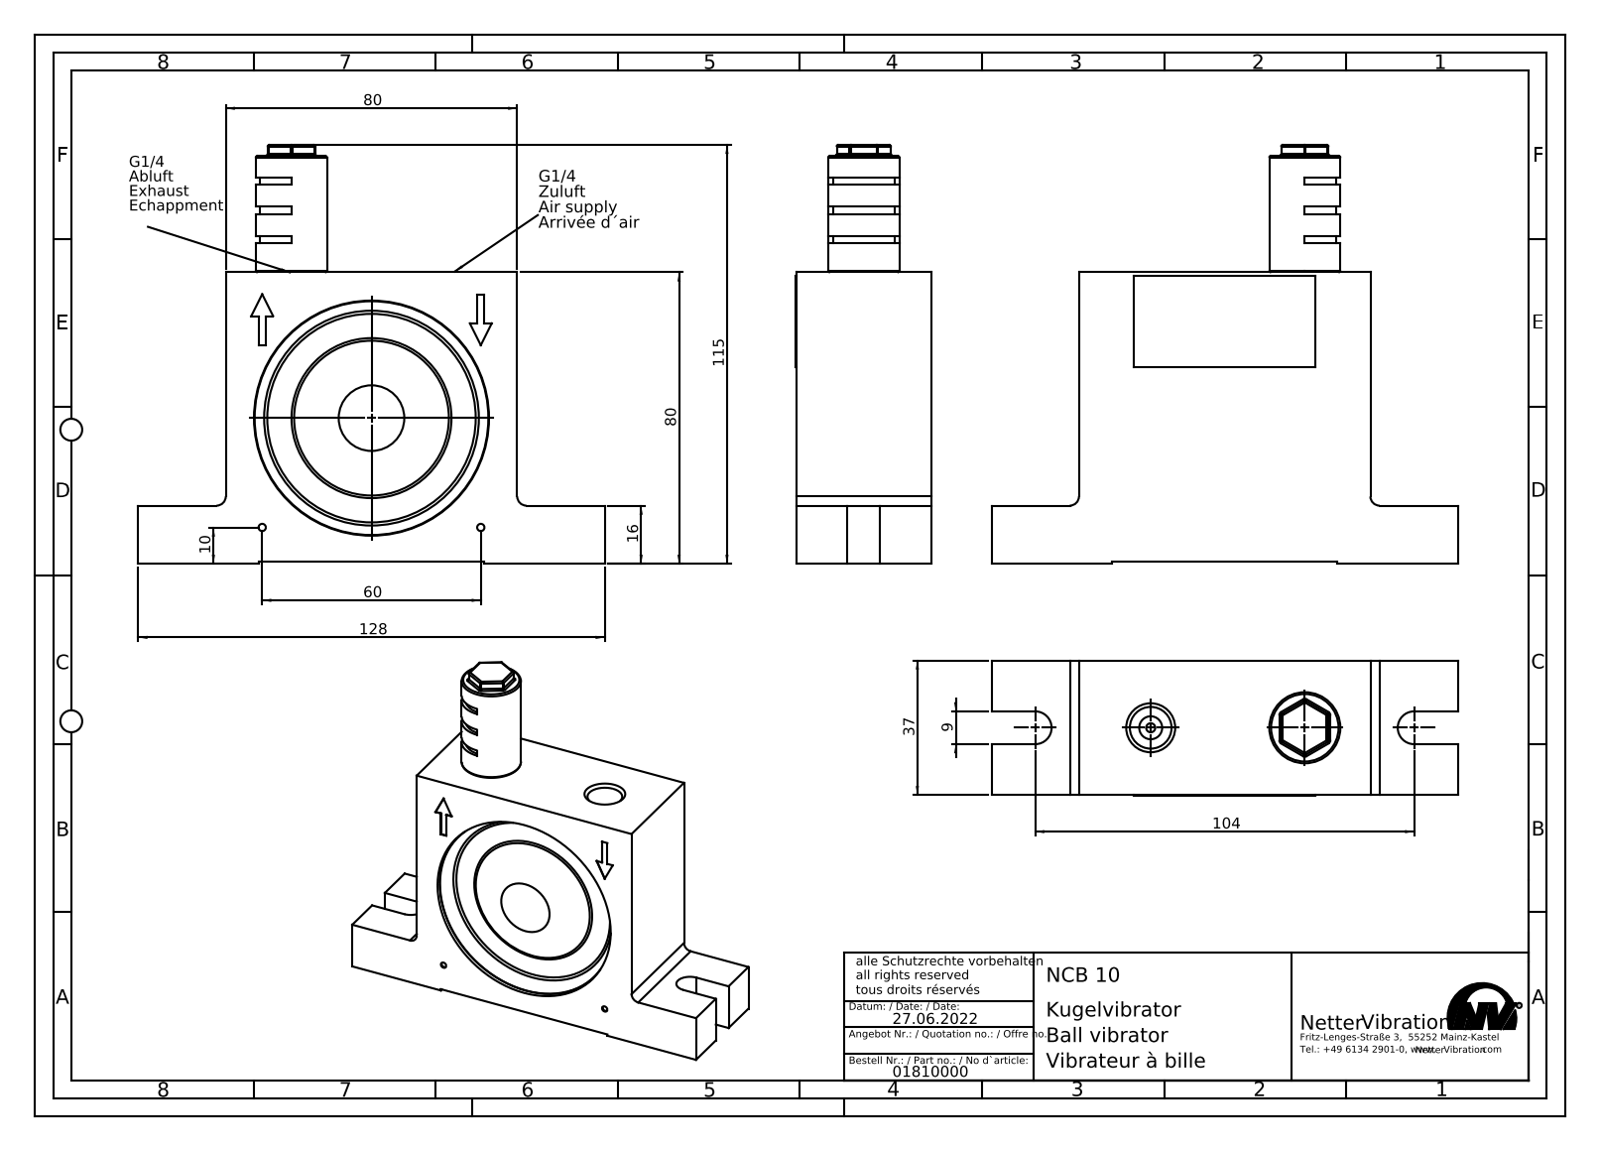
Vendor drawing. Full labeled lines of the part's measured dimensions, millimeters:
Part name (STEP PRODUCT): NCB 10 Kugelvibrator # 01810000
STEP written by: SolidWorks 2015 (AUTOMOTIVE_DESIGN)
Units: millimetres
Bodies: 3 solids, 232 faces (104 planar, 54 cylindrical, 74 other)
Overall size (bounding box): 128 × 115 × 37
Volume: 186 852 mm³ · Surface area: 47 803 mm²
Round holes (diameter × count): ⌀2 ×2, ⌀11.45 ×2, ⌀2.5 ×1, ⌀4.1 ×1, ⌀10 ×1, ⌀55 ×1, ⌀62 ×1, ⌀64.5 ×1
Round bosses / shafts (diameter × count): ⌀19.5 ×1, ⌀13.16 ×1
Partial cylindrical surfaces — rounded edges, fillets, slot ends (radius × count): R0.5 ×18, R2.5 ×2, R4.5 ×2, R8.5 ×1
Main face-to-face distances: 80, 37, 79.5, 0.5, 6.85, 7.15, 16, 15.5, 64, 8.5
Hole centre spacings: 42.43, 65.92, 28.7, 42.3, 60
